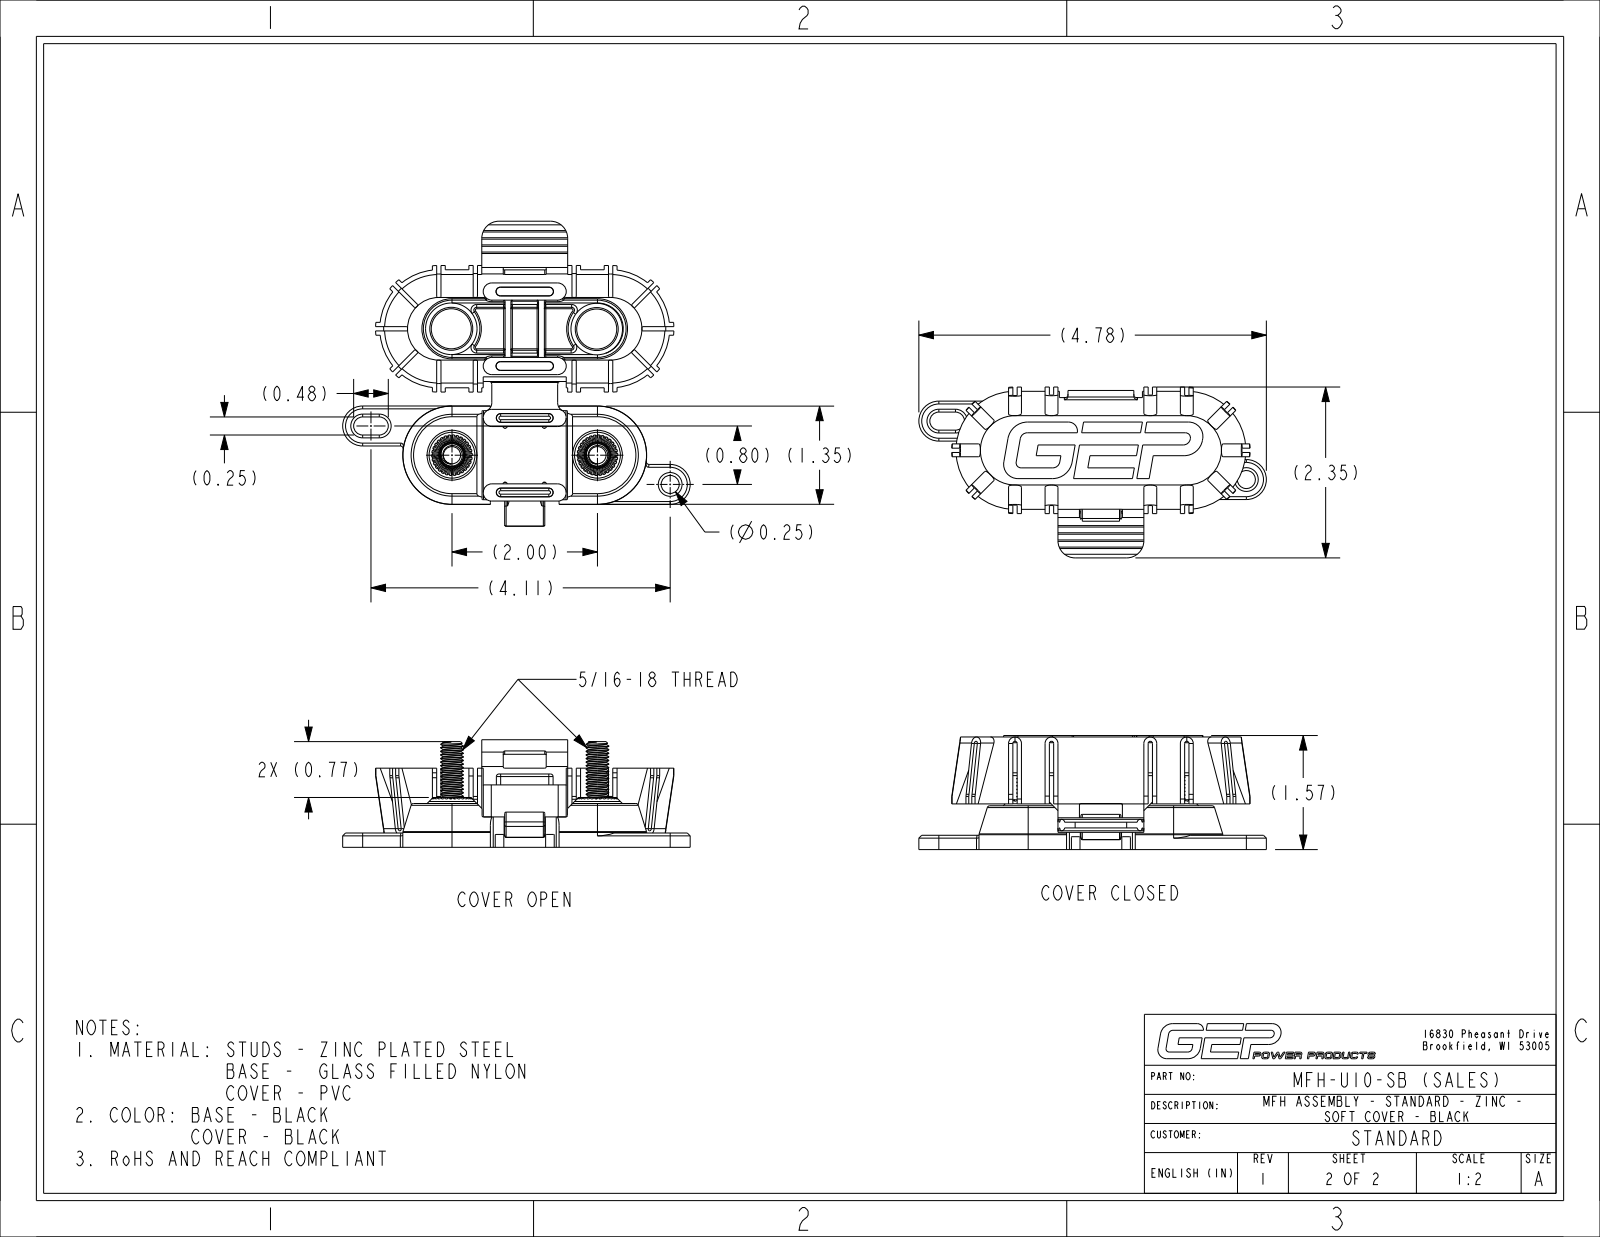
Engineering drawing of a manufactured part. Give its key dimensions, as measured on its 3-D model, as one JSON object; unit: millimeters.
{"part_name": "MFH-UXX-XX_BODY_NCF; C05-1003-U1_NCF; MFH-SB_NCF_INSTALLED; MFH-U10-SB_INSTALLED_NCF_ASM", "step_written_by": "CREO PARAMETRIC BY PTC INC, 2024014 (CONFIG_CONTROL_DESIGN)", "units": "millimeters", "bodies": {"solids": 4, "faces": 2099, "planar": 769, "cylindrical": 729, "other": 601}, "overall_size": [121.4, 59.6, 39.8], "volume_mm3": 51930, "surface_area_mm2": 54060, "round_holes": [[9, 2], [15, 2], [6.3, 1]], "round_bosses_or_shafts": [[16, 2], [8, 2]], "partial_cylinders_radius": [[0.4, 236], [0.5, 24], [1, 20], [0.5, 14], [0.4, 13], [1.5, 12], [0.3, 10], [0.9, 10]], "face_to_face_distances": [1.5, 3, 2, 4.5, 10.7, 0.5, 15.2, 26, 12.2, 13.7], "hole_center_spacings": [50.8, 27.4, 27.6, 50.5, 51.1, 76.9, 77.1]}
